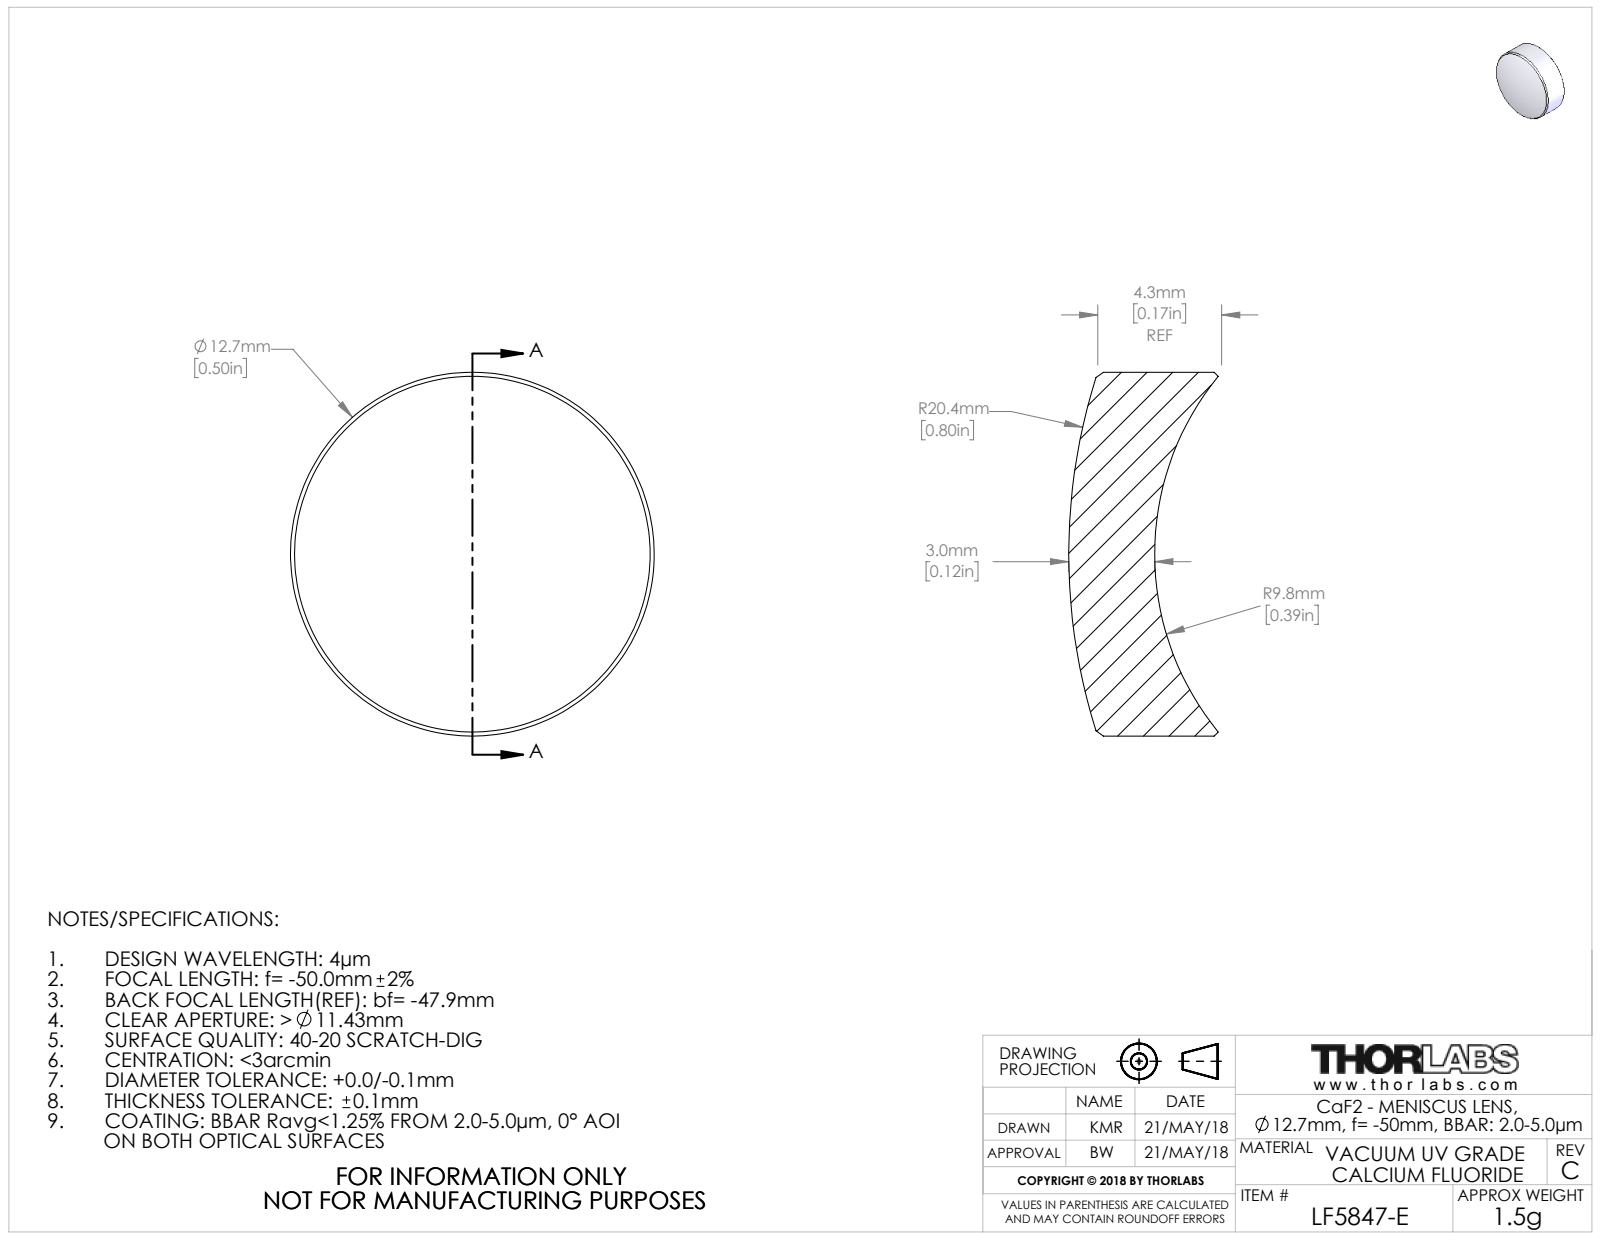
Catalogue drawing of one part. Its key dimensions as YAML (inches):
part_name: "20182-E0W"
step_written_by: "SolidWorks 2016 (CONFIG_CONTROL_DESIGN)"
units: inches
bodies: {solids: 1, faces: 10, planar: 0, cylindrical: 2, other: 8}
overall_size: [0.5, 0.5, 0.206]
volume: 0.028
surface_area: 0.672
round_bosses_or_shafts:
  - {diameter: 0.5, count: 1}
